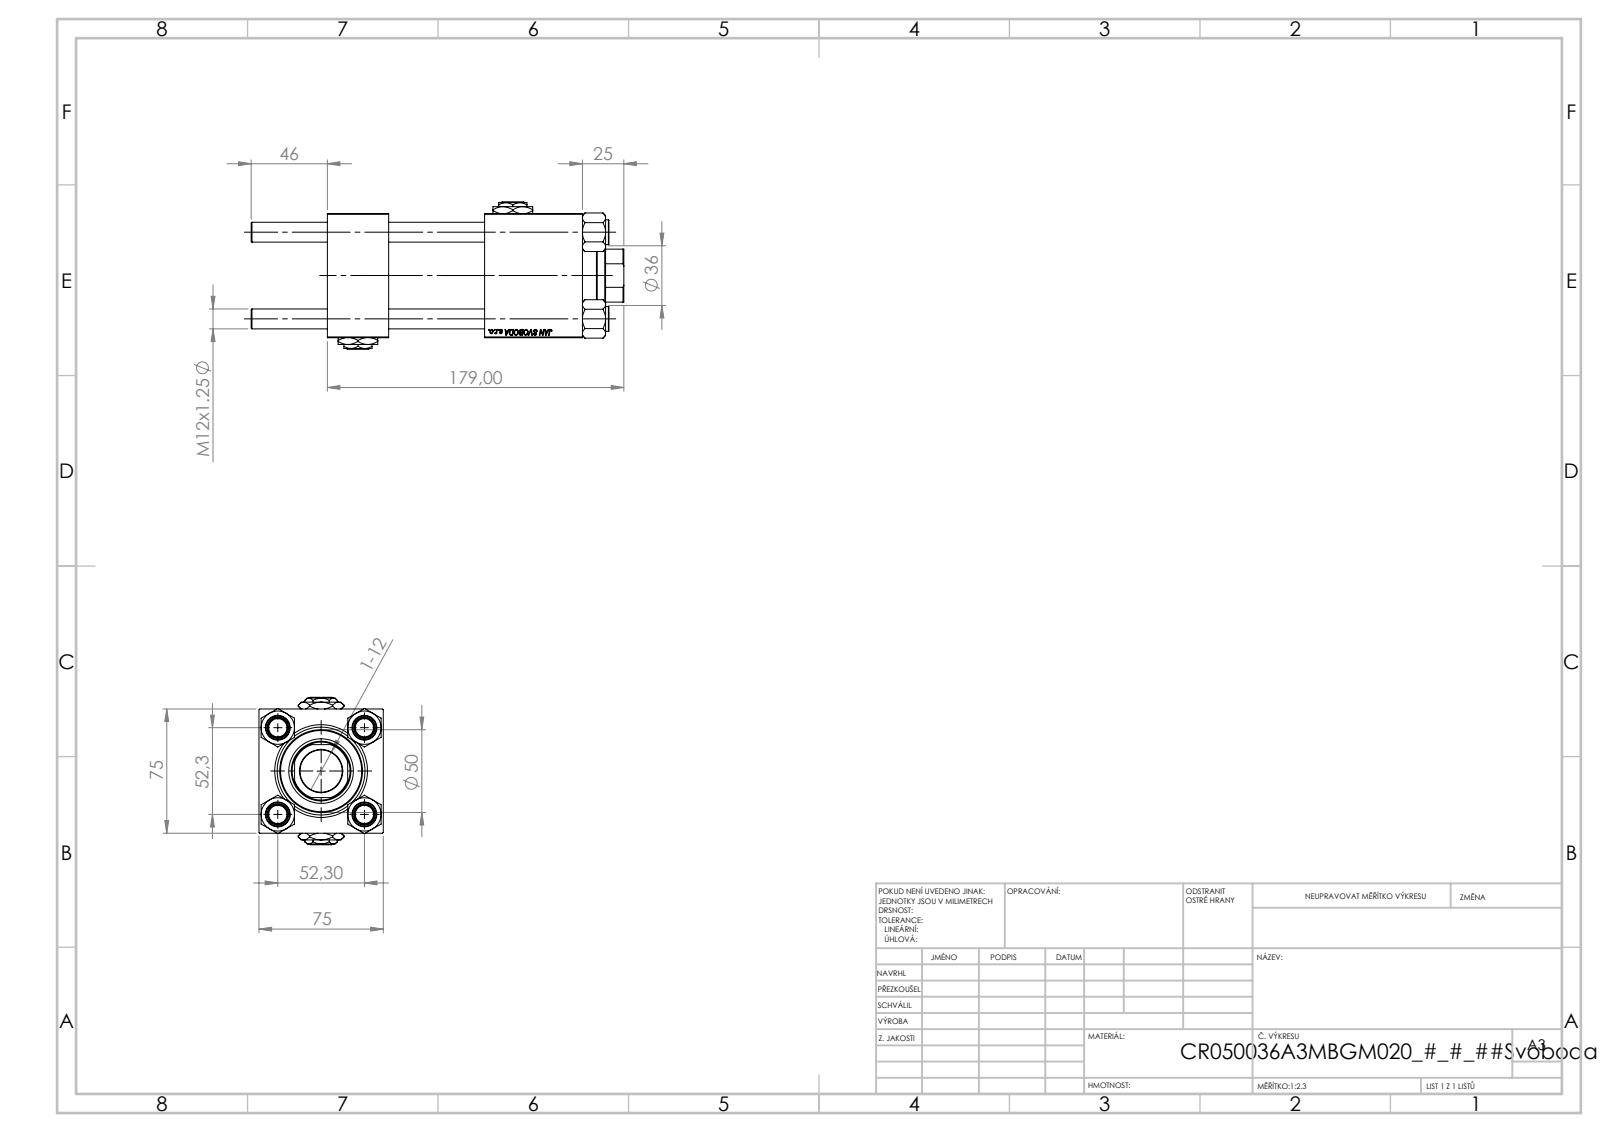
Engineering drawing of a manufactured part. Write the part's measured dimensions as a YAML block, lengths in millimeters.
part_name: "V215_VC_A; V215CR_BODY_A; Zatka_pro_OIL_PORT; V215CR_VCP (+2 more)"
step_written_by: "SolidWorks 2019 (CONFIG_CONTROL_DESIGN)"
units: millimeters
bodies: {solids: 13, faces: 1233, planar: 567, cylindrical: 88, other: 578}
overall_size: [225, 89, 75]
volume: 714043
surface_area: 176424
round_holes:
  - {diameter: 12, count: 4}
  - {diameter: 7, count: 2}
  - {diameter: 20.96, count: 2}
  - {diameter: 30, count: 2}
  - {diameter: 25.5, count: 1}
  - {diameter: 36, count: 1}
  - {diameter: 39, count: 1}
  - {diameter: 41, count: 1}
  - {diameter: 53, count: 1}
round_bosses_or_shafts:
  - {diameter: 15, count: 4}
  - {diameter: 56, count: 1}
  - {diameter: 50, count: 1}
partial_cylinders:
  - {radius: 17.5, count: 1}
face_to_face_distances: [75, 37, 95, 154, 117, 59, 58, 74.8, 125.3, 88.3]
hole_center_spacings: [36.98, 52.3, 73.96, 93.5]
